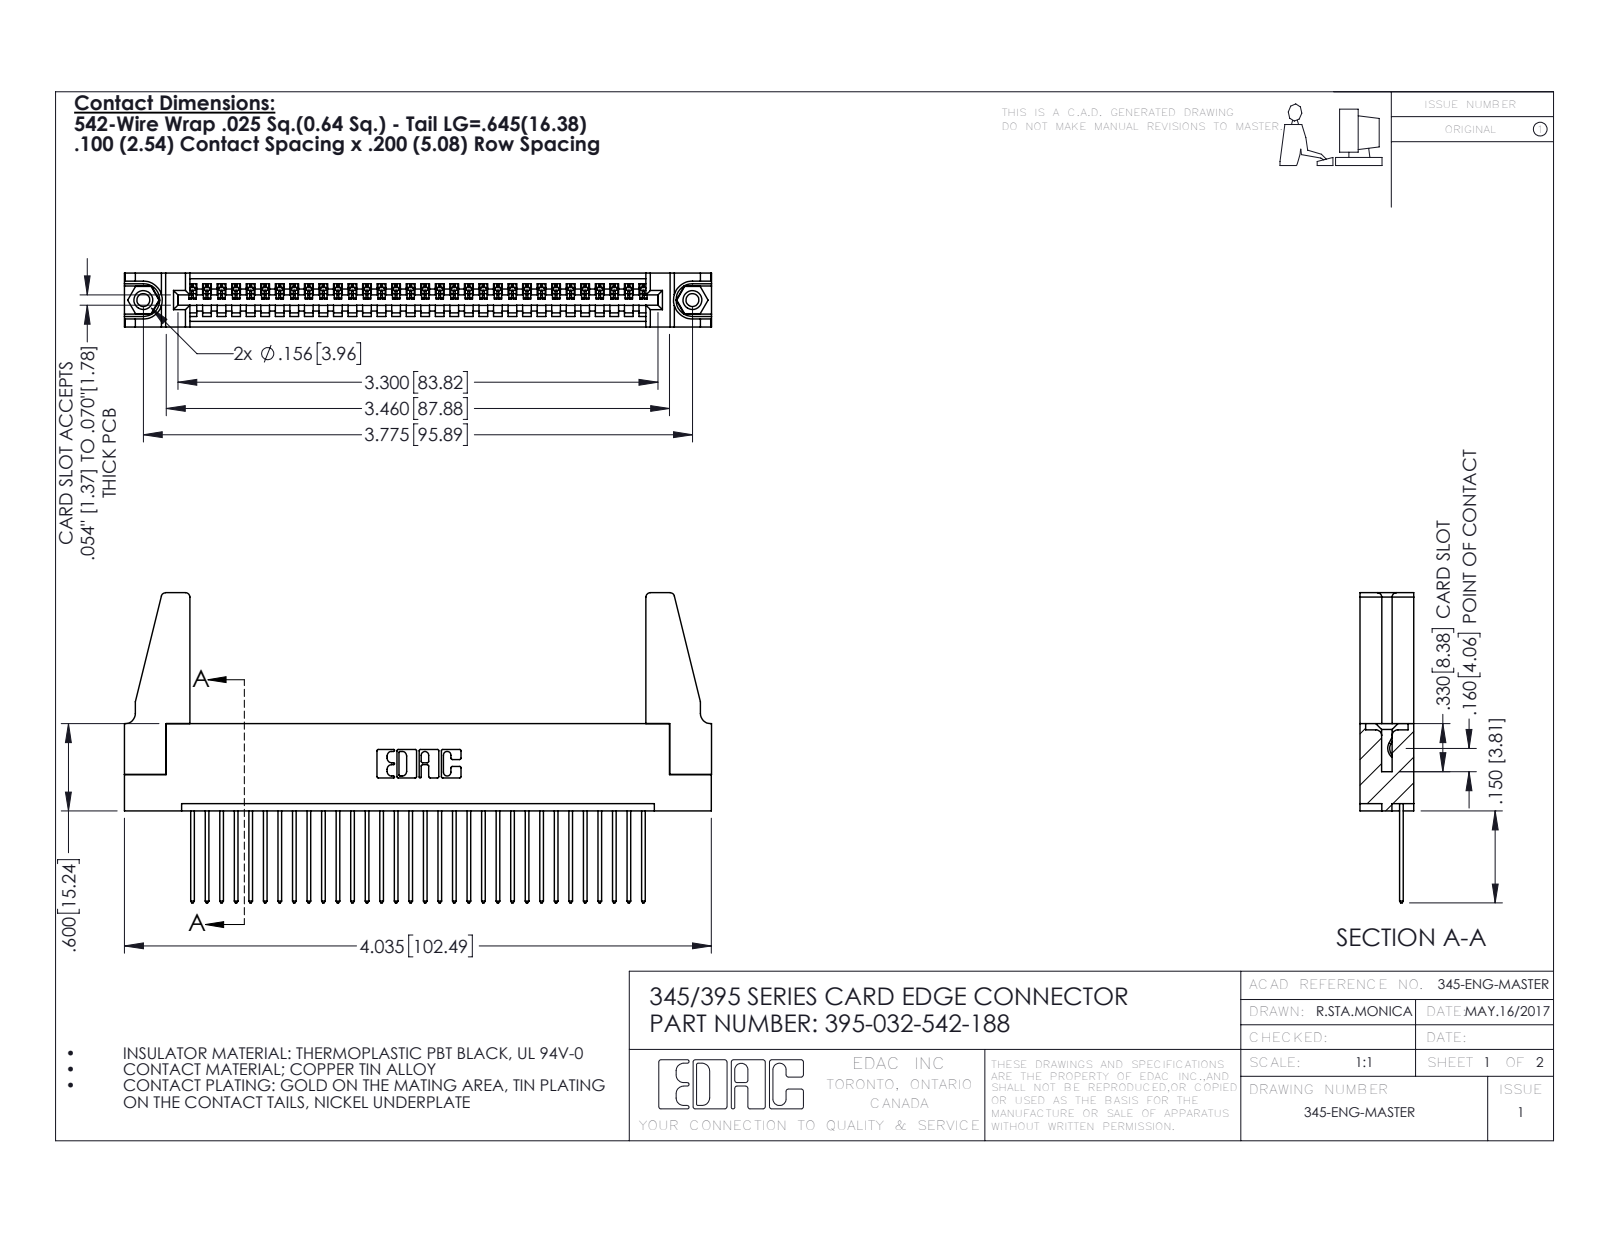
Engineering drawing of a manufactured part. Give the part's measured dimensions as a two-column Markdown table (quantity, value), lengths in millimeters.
| quantity | value |
| --- | --- |
| part name | 395-032-542-188; 345 Part_Flush Mounting Lugs - 0.156 Dia-TH; 345-250-001_345-250-001-102; 345-220-078_345-220-088 (+1 more) |
| STEP written by | SolidWorks 2016 (CONFIG_CONTROL_DESIGN) |
| units | millimeters |
| bodies | 37 solids, 2106 faces (1432 planar, 658 cylindrical, 16 other) |
| overall size | 102.5 × 54.2 × 9.4 |
| volume | 13 000 mm³ |
| surface area | 16 370 mm² |
| round holes (diameter × count) | 2.3 × 2, 3.2 × 2, 4 × 2, 1.6 × 1 |
| round bosses / shafts (diameter × count) | 3.9 × 2 |
| partial cylindrical surfaces (radius × count) | 0.2 × 64, 0.3 × 64, 0.3 × 22, 0.8 × 8, 0.2 × 6, 0.8 × 6, 0.7 × 3, 0.8 × 2 |
| main face-to-face distances | 1.8, 7.6, 9.4, 5.1, 2.5, 6.9, 0.6, 5.7, 3.8, 1.8 |
| hole center spacings | 6.9, 89.9, 95.9 |
